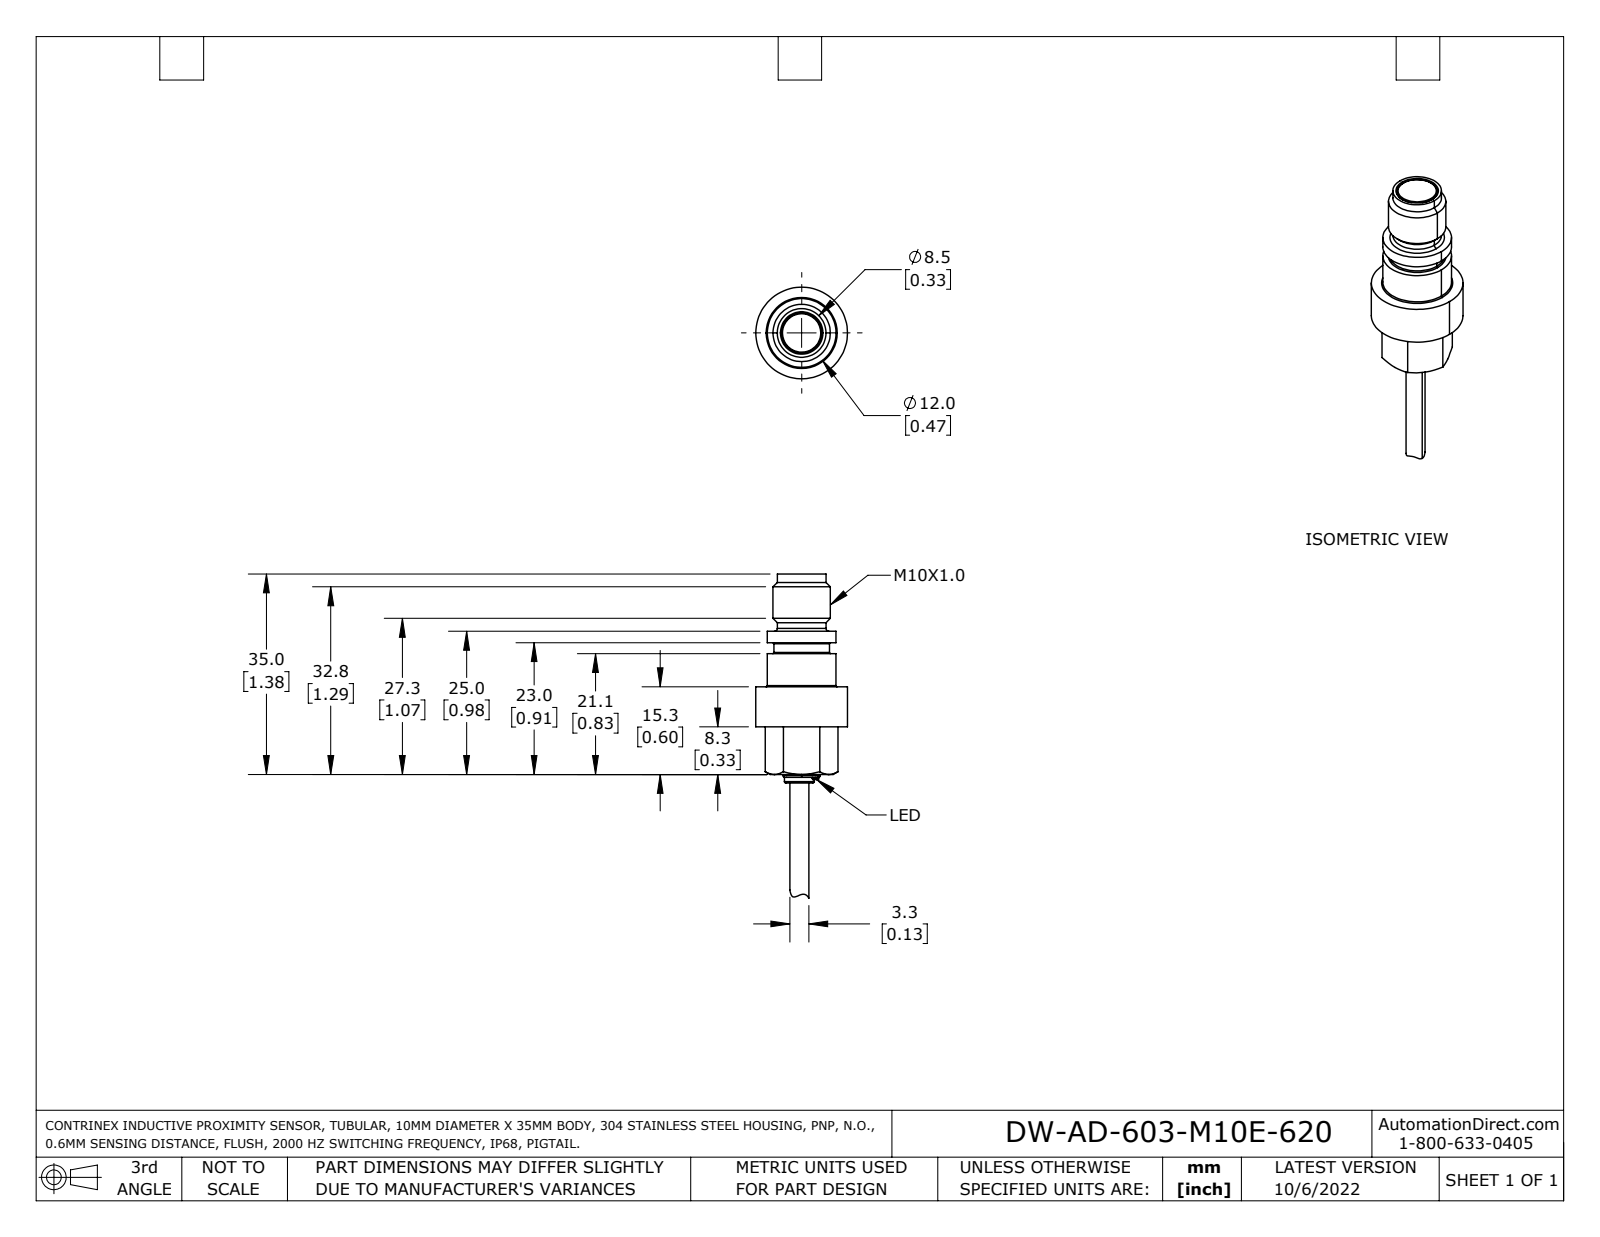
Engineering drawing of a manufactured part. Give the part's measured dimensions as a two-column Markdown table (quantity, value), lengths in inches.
| quantity | value |
| --- | --- |
| part name | DW-AD-603-M10E-620 |
| STEP written by | SolidWorks 2021 (AUTOMOTIVE_DESIGN) |
| units | inches |
| bodies | 1 solid, 99 faces (43 planar, 24 cylindrical, 32 other) |
| overall size | 2.228 × 0.63 × 0.63 |
| volume | 0.257 in³ |
| surface area | 3.144 in² |
| round bosses / shafts (diameter × count) | 0.63 × 1, 0.472 × 1, 0.394 × 1, 0.382 × 1, 0.335 × 1, 0.276 × 1, 0.256 × 1, 0.205 × 1 |
| partial cylindrical surfaces (radius × count) | 0.012 × 2, 0.116 × 1 |
| main face-to-face distances | 0.433, 0.276, 0.602, 0.327, 0.776, 1.051, 1.378, 0.394, 0.382, 0.657 |
